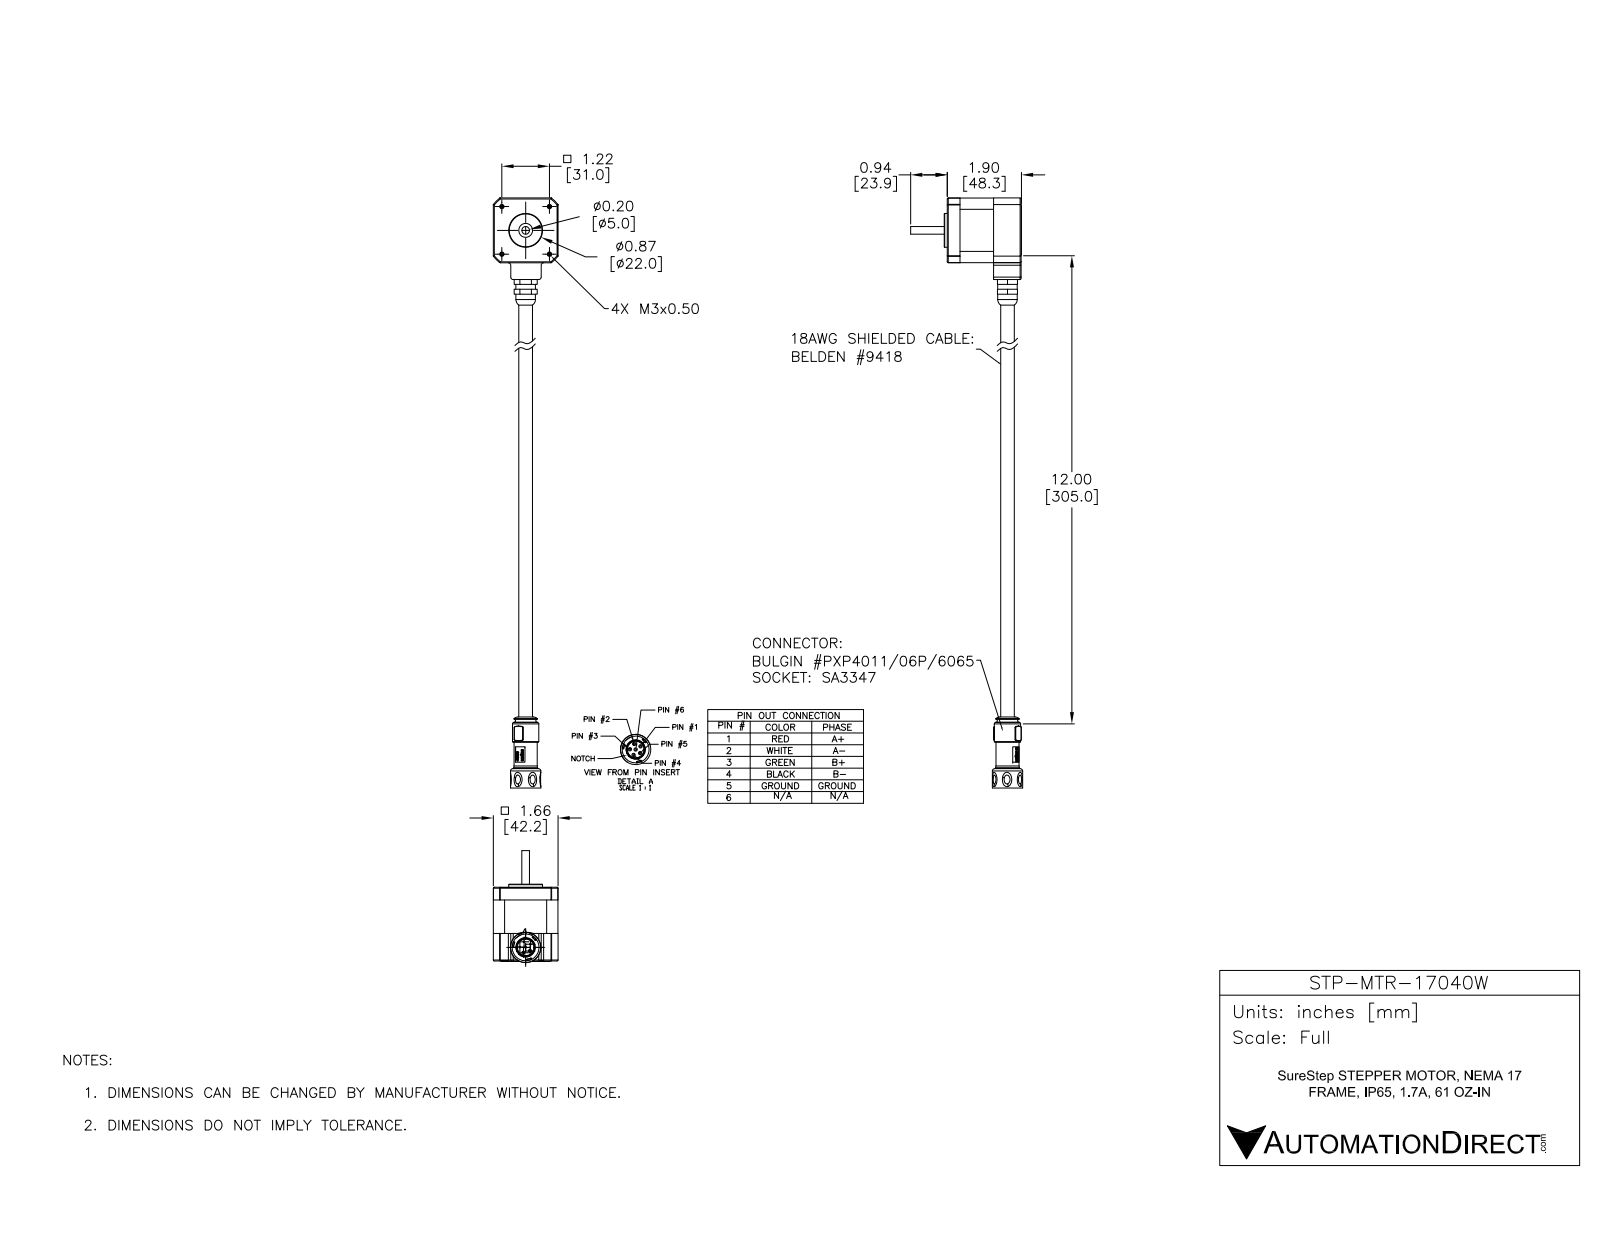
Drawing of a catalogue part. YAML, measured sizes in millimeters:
part_name: "STP-MTR-17040W"
step_written_by: "SolidWorks 2017 (AUTOMOTIVE_DESIGN)"
units: millimeters
bodies: {solids: 7, faces: 847, planar: 301, cylindrical: 237, other: 309}
overall_size: [384, 72.9, 42.2]
volume: 114000
surface_area: 29120
round_holes:
  - {diameter: 1.2, count: 6}
  - {diameter: 2.2, count: 4}
  - {diameter: 3.8, count: 4}
  - {diameter: 3.2, count: 1}
  - {diameter: 5.8, count: 1}
  - {diameter: 9, count: 1}
  - {diameter: 11.1, count: 1}
  - {diameter: 11.4, count: 1}
  - {diameter: 17.5, count: 1}
round_bosses_or_shafts:
  - {diameter: 3.3, count: 4}
  - {diameter: 1.3, count: 4}
  - {diameter: 31.8, count: 1}
  - {diameter: 22, count: 1}
  - {diameter: 19.7, count: 1}
  - {diameter: 17.1, count: 1}
  - {diameter: 15.6, count: 1}
  - {diameter: 15, count: 1}
partial_cylinders:
  - {radius: 0.1, count: 28}
  - {radius: 0.6, count: 19}
  - {radius: 0.5, count: 12}
  - {radius: 9.9, count: 6}
  - {radius: 1.6, count: 4}
  - {radius: 7.3, count: 3}
  - {radius: 2.3, count: 1}
  - {radius: 4, count: 1}
face_to_face_distances: [42.1, 42.2, 42.1, 48, 48.3, 30.4, 10.9, 11, 53, 53.1]
hole_center_spacings: [3.8, 7.1, 3.8, 21.9, 31, 4.4, 4.4, 21.8]
